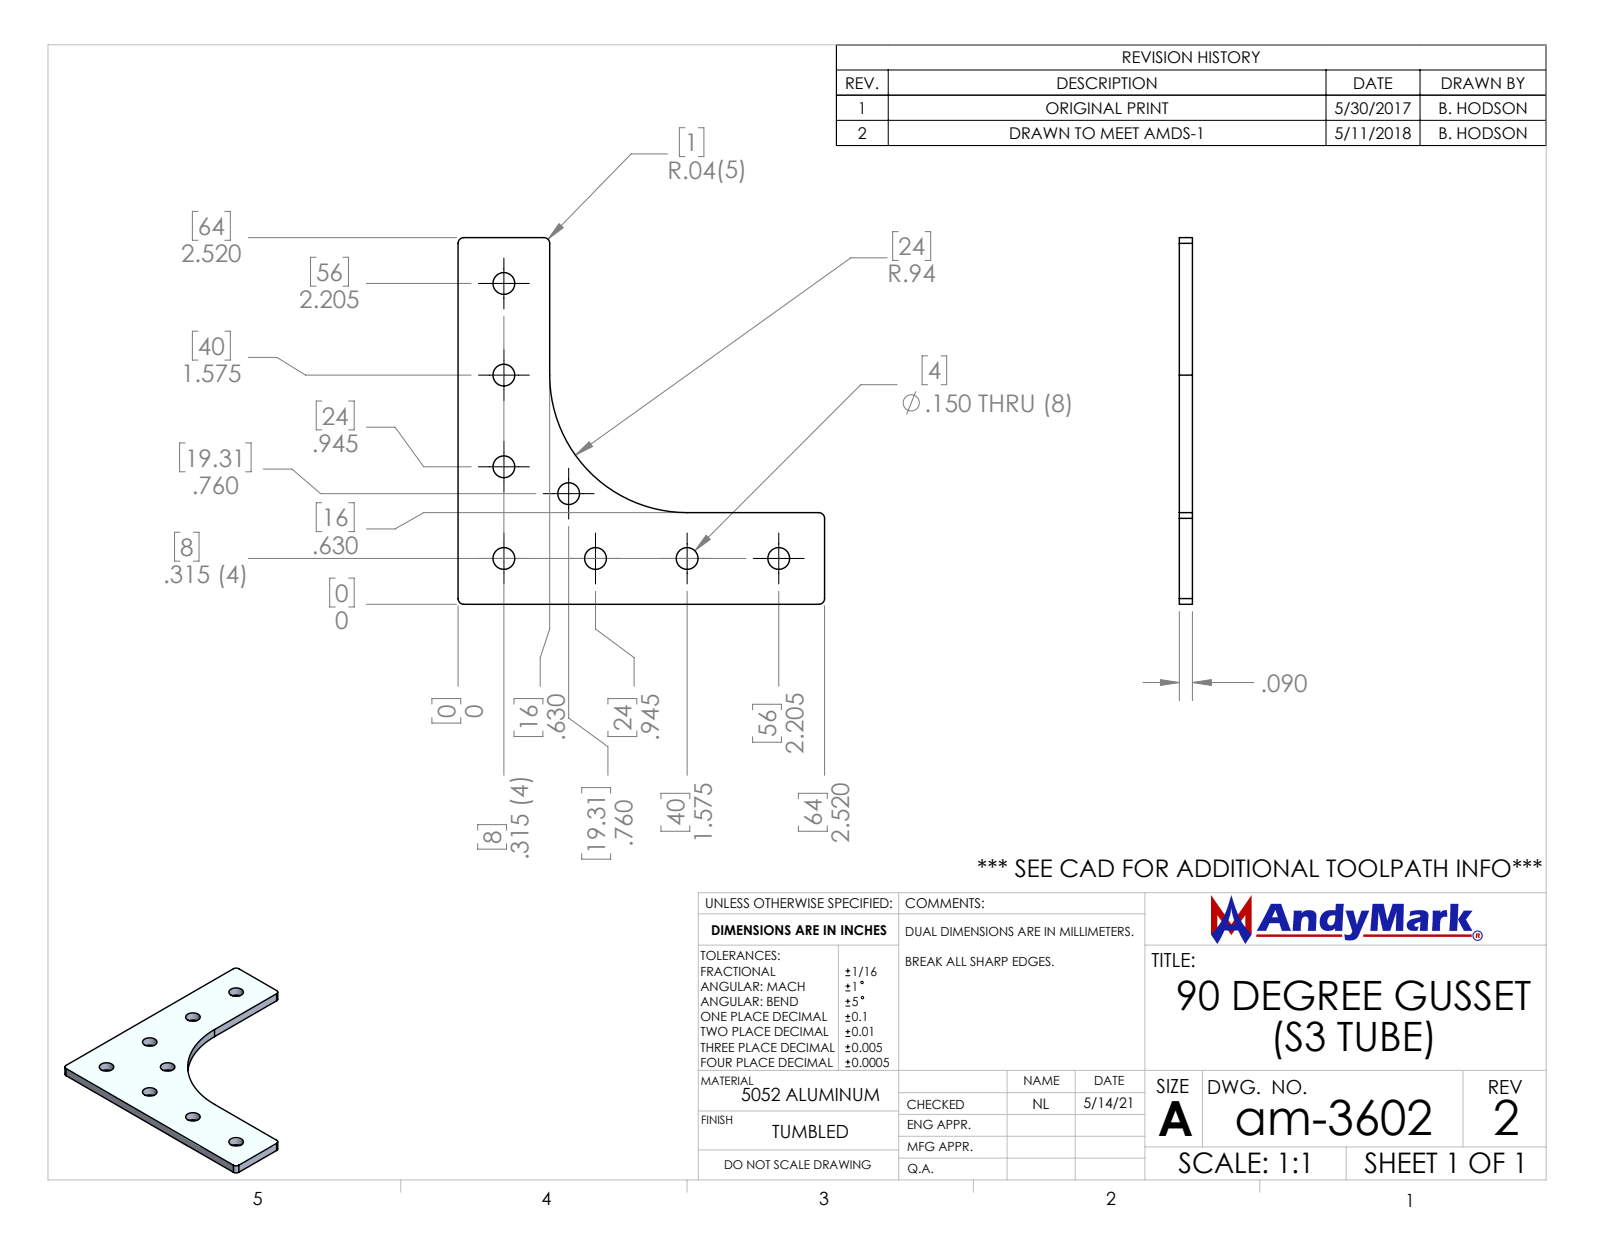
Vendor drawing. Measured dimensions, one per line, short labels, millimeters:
name: am-3602 90 Degree Gusset (S3 Tube) REV2
written by: SolidWorks 2019 (AUTOMOTIVE_DESIGN)
unit: mm
bodies: 1 solid, 22 faces (8 planar, 14 cylindrical, 0 other)
size: 64 × 64 × 2.29
volume: 4 168 mm³; area: 4 422 mm²
holes: 8× ⌀3.81
rounds: 5× R1, 1× R24
face distances: 2.29, 16, 64, 48
hole spacings: 16, 32, 12.24, 23.58, 35.78, 38.39, 48, 50.6
